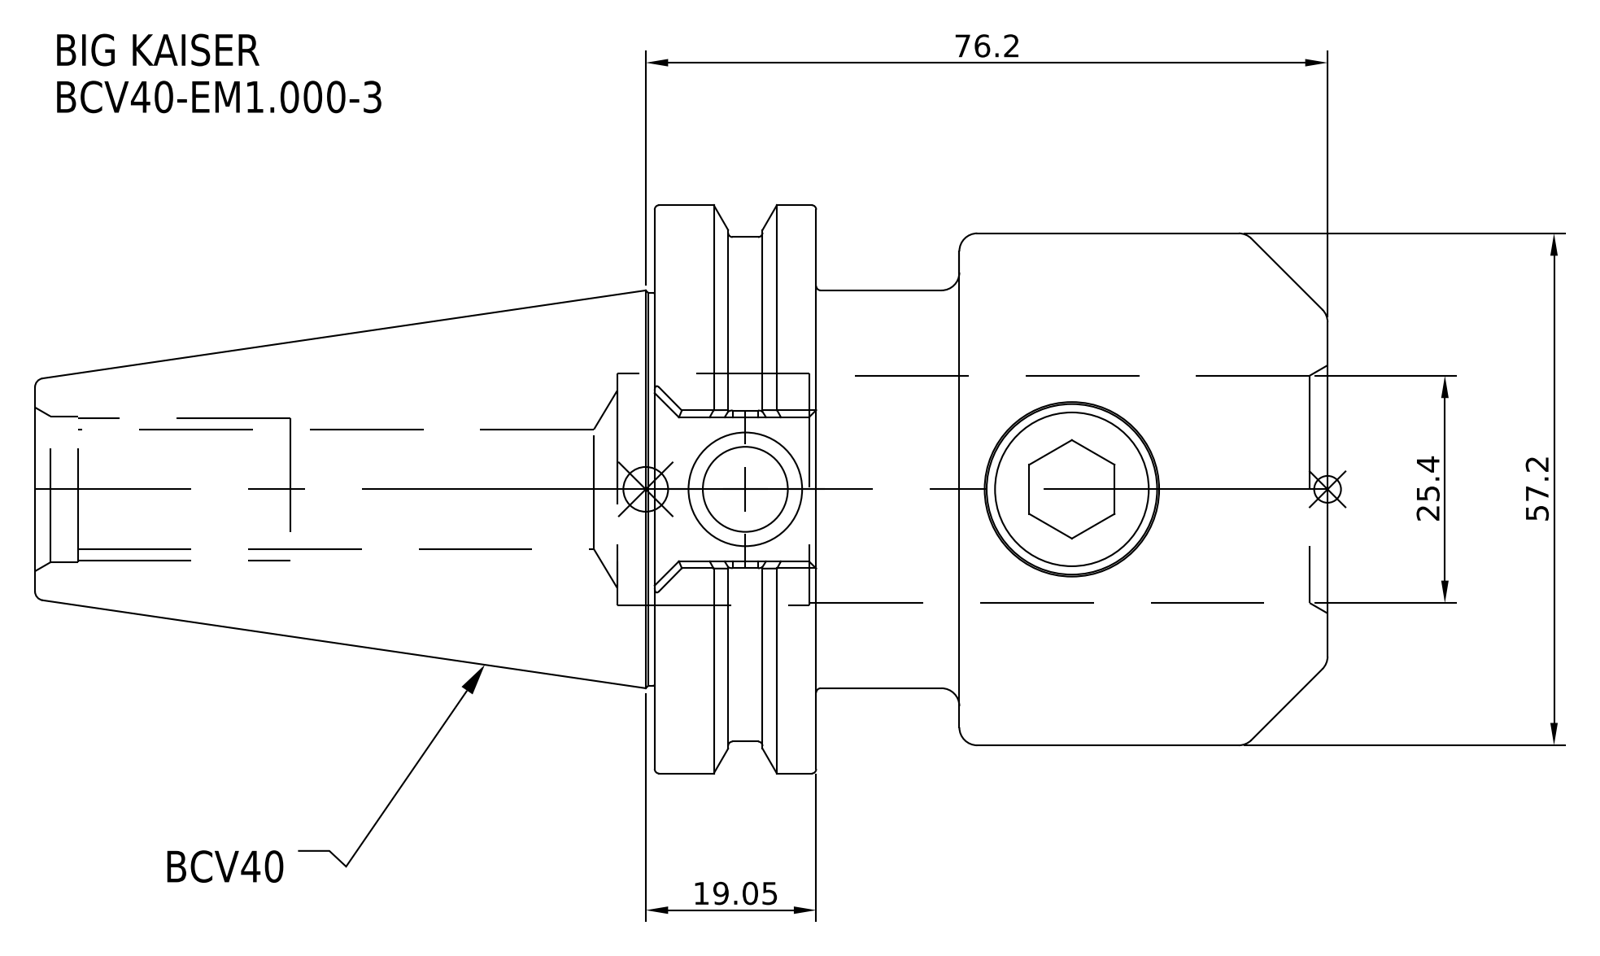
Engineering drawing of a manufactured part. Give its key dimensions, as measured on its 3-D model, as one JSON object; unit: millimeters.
{"part_name": "BCV40-EM_1_000-3", "step_written_by": "SolidWorks 2021 (CONFIG_CONTROL_DESIGN)", "units": "millimeters", "bodies": {"solids": 1, "faces": 30, "planar": 8, "cylindrical": 14, "other": 8}, "overall_size": [144.45, 63.5, 63.5], "volume_mm3": 223898, "surface_area_mm2": 31136, "round_holes": [[25.4, 1]], "round_bosses_or_shafts": [[63.5, 1], [57.2, 1], [56.36, 1], [44.45, 1]], "face_to_face_distances": [18.05, 16, 34.05, 41.15, 57.15, 75.2, 144.45, 103.3, 87.3, 69.25]}
